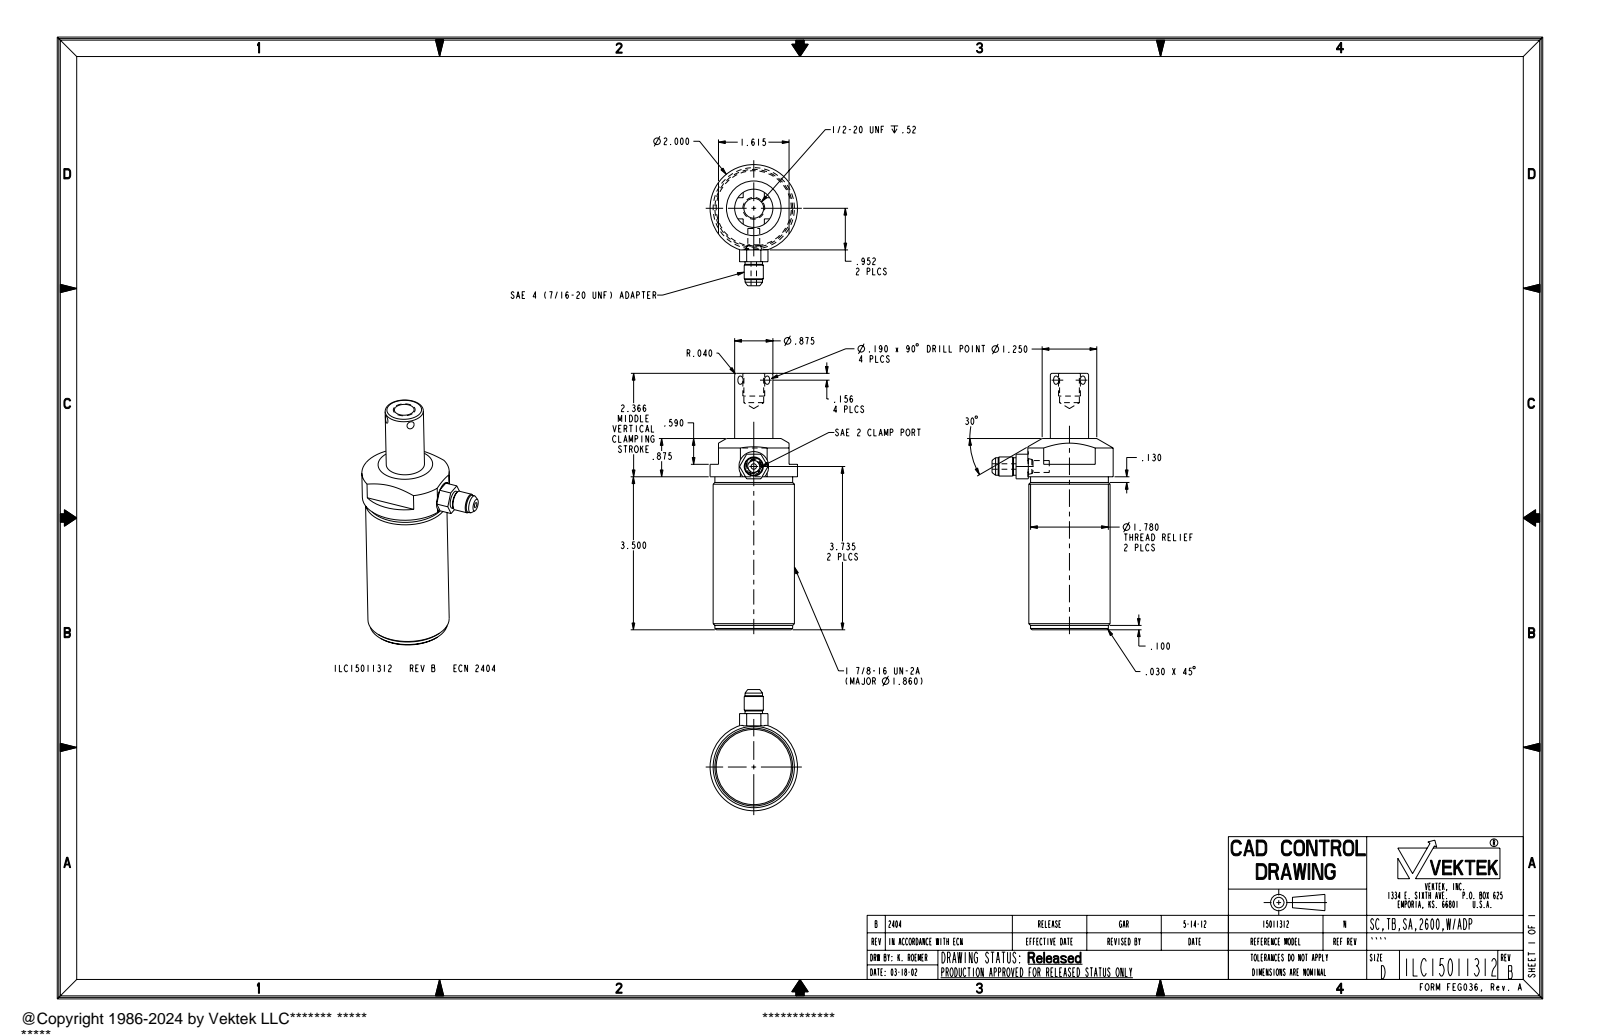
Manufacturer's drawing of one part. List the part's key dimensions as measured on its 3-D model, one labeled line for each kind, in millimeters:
Part name (STEP PRODUCT): ILC15011312
STEP written by: PRO/ENGINEER BY PARAMETRIC TECHNOLOGY CORPORATION, 2007460 (AUTOMOTIVE_DESIGN_CC2)
Units: millimetres
Bodies: 1 solid, 81 faces (25 planar, 26 cylindrical, 30 other)
Overall size (bounding box): 149 × 70.4 × 50.8
Volume: 208 400 mm³ · Surface area: 25 310 mm²
Round holes (diameter × count): ⌀3.2 ×1, ⌀6.9 ×1, ⌀11.5 ×1
Round bosses / shafts (diameter × count): ⌀50.8 ×1, ⌀47.2 ×1, ⌀45.2 ×1, ⌀22.2 ×1, ⌀12.7 ×1, ⌀11.1 ×1, ⌀10.2 ×1
Partial cylindrical surfaces — rounded edges, fillets, slot ends (radius × count): R8.7 ×1
Main face-to-face distances: 88.9, 111.1, 22.2, 41, 149, 60.1, 37.9, 96.1, 7.2, 15
